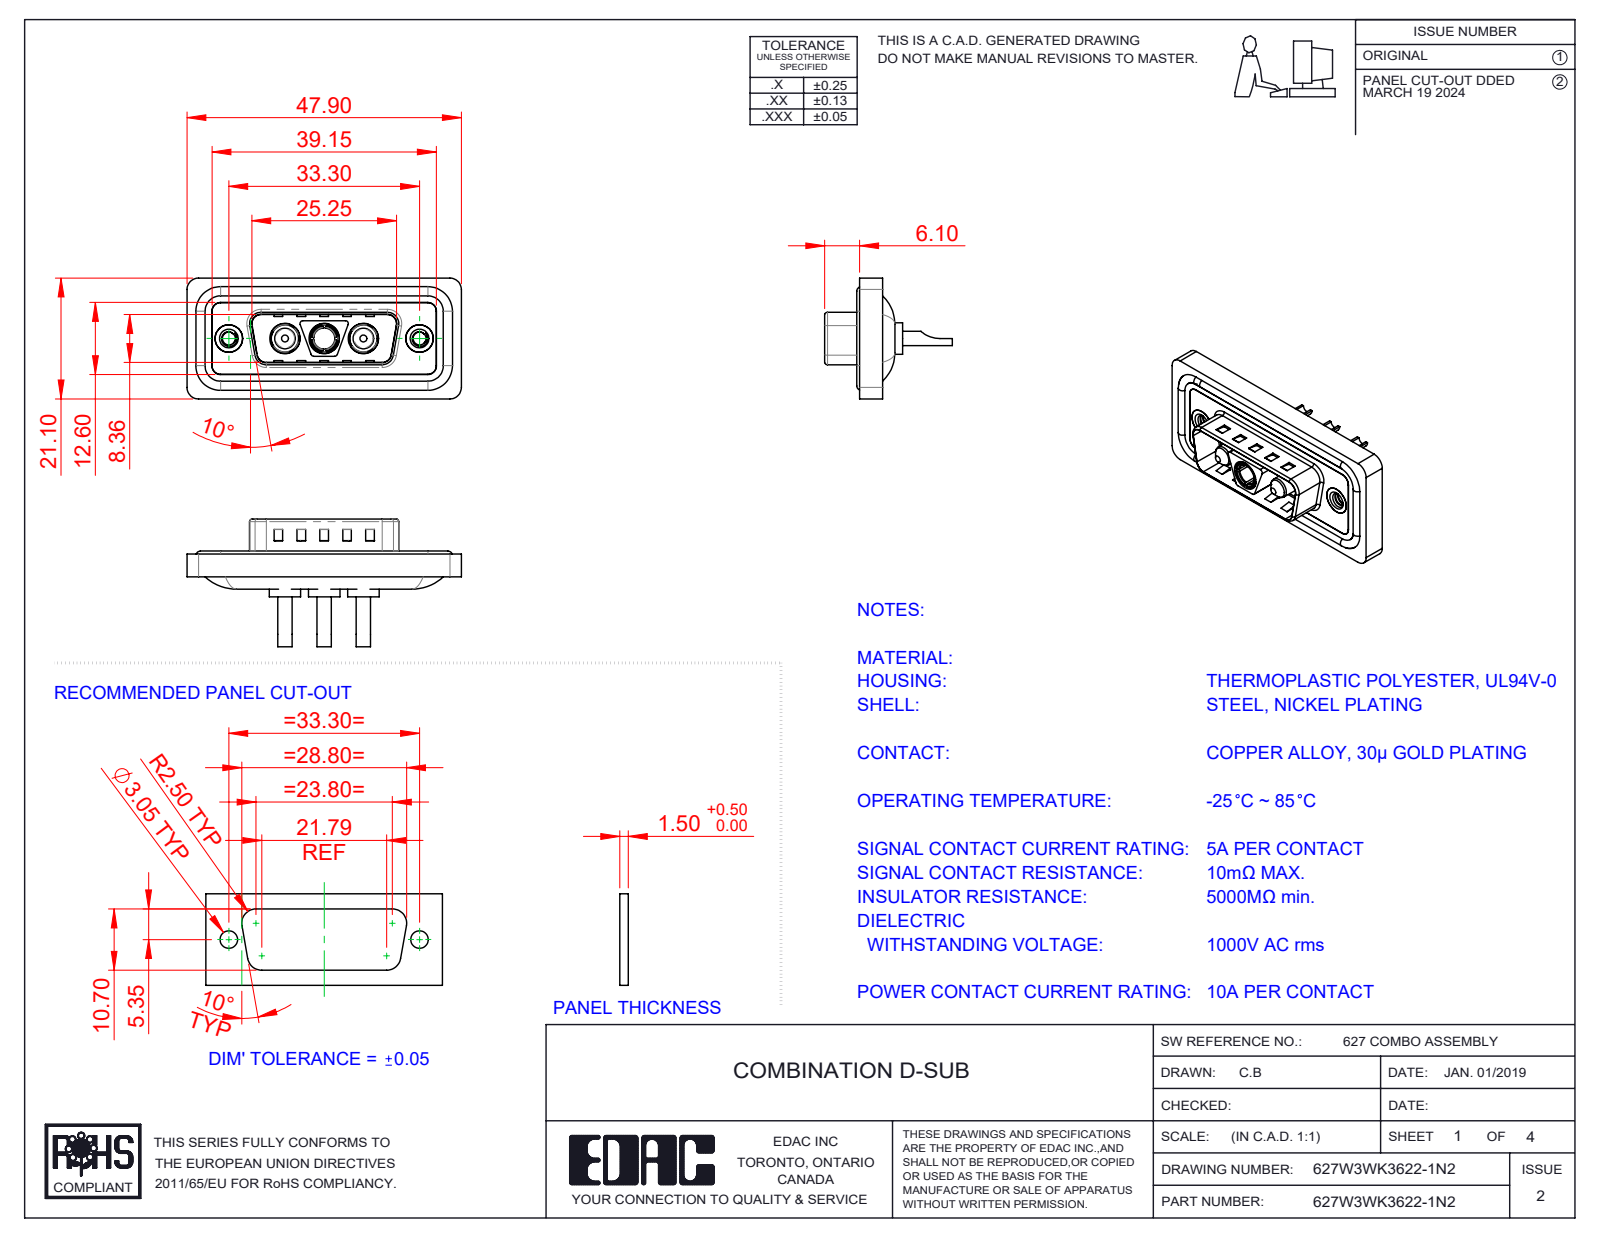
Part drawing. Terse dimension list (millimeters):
name: 627Combo Shell Front_15 Contacts; 627Combo Threaded Rivet_2; Power Socket_10A SC; Power Pin_10A SC (+4 more)
written by: SolidWorks 2023 (CONFIG_CONTROL_DESIGN)
unit: mm
bodies: 13 solids, 627 faces (237 planar, 259 cylindrical, 131 other)
size: 47.9 × 22.3 × 21.1
volume: 5 680 mm³; area: 9 270 mm²
holes: 3× ⌀1.7, 3× ⌀4.85, 3× ⌀5.3, 2× ⌀2.26, 2× ⌀4, 2× ⌀4.8, 2× ⌀5, 1× ⌀3.7
bosses: 4× ⌀1.6, 3× ⌀5.5, 3× ⌀5.2, 3× ⌀4.75, 3× ⌀3.75, 3× ⌀2.5, 2× ⌀4.9, 2× ⌀3.6
rounds: 26× R1.5, 20× R2, 12× R0.5, 8× R1.6, 4× R0.25, 4× R0.6, 4× R0.65, 4× R0.9
face distances: 0.4, 1.1, 1.5, 0.5, 1.6, 3.1, 2.9, 4, 0.82, 9.58
hole spacings: 6.85, 9.8, 16.65, 23.5, 13.7, 33.3
